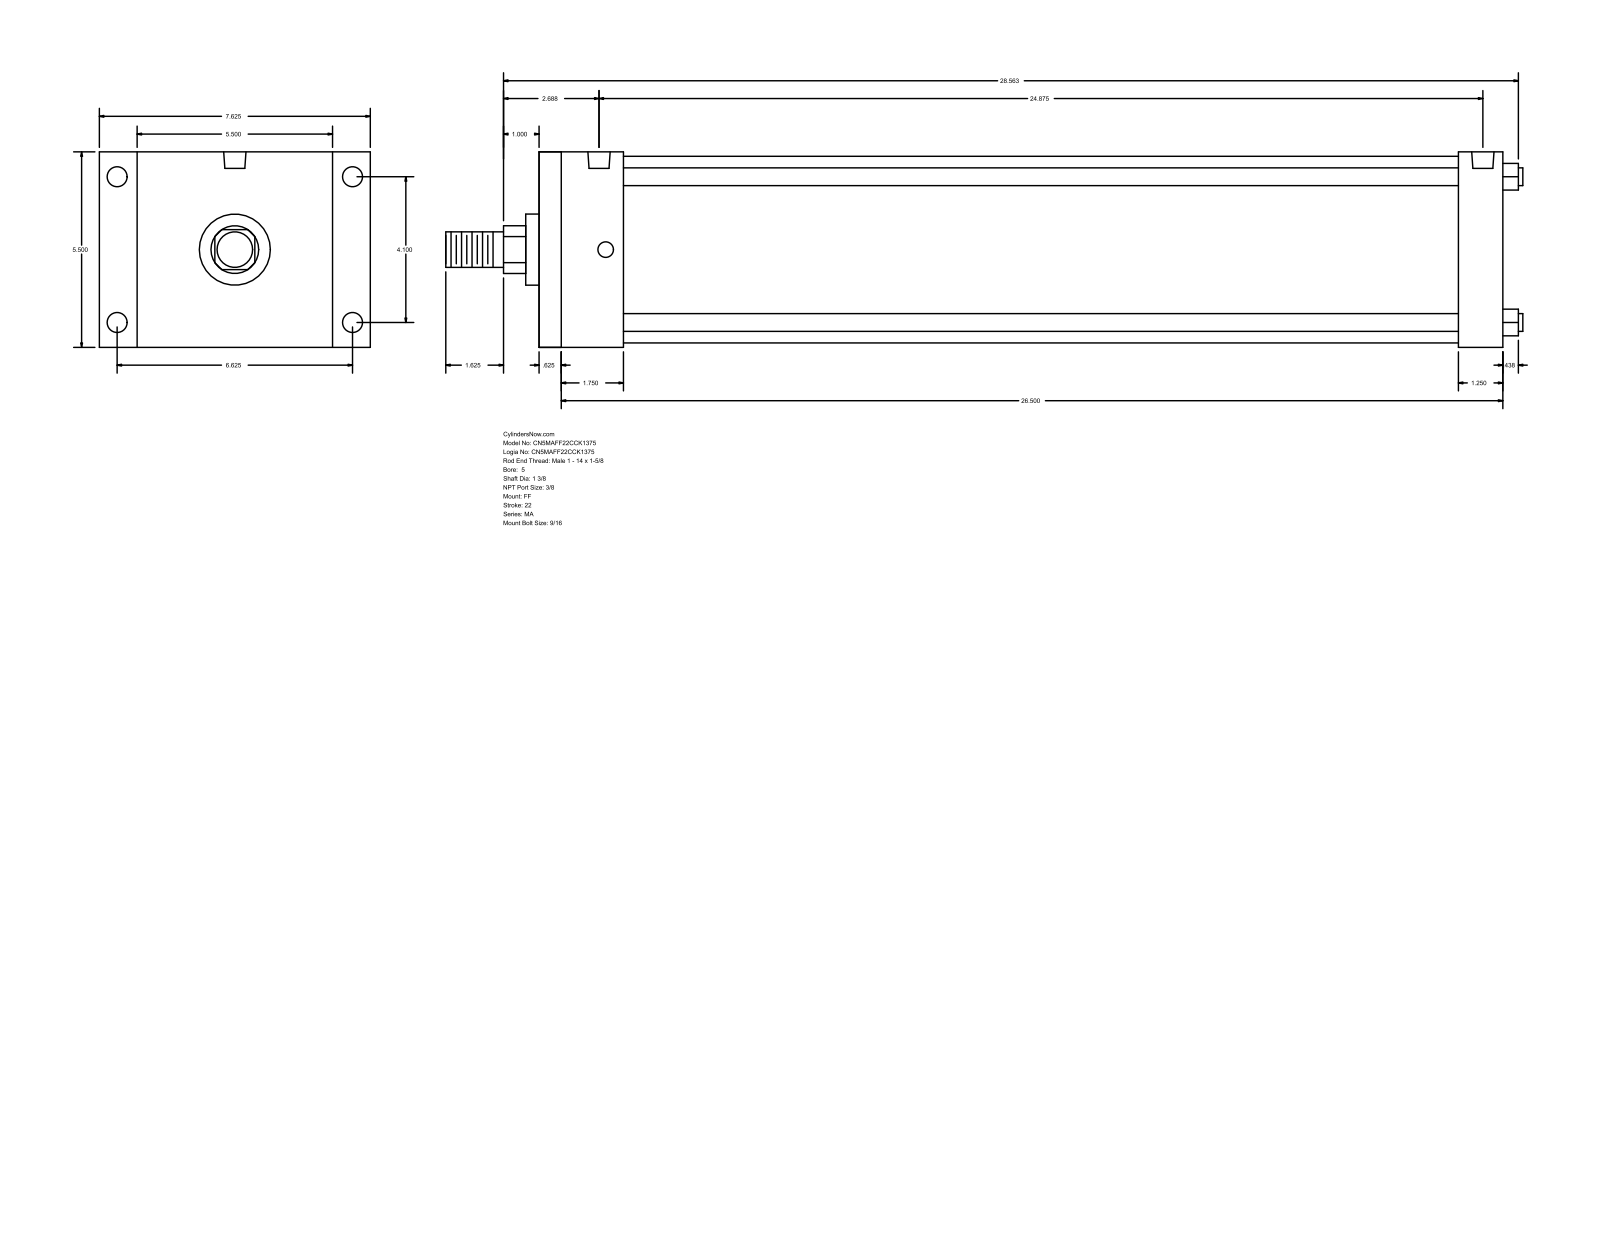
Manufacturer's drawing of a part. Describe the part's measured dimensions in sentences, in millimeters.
The part is named "MA_FF__0500_1.375". Its 3-D file was written by "GSSL Pune (CONFIG_CONTROL_DESIGN)". It is 0 solids with 92 faces: 64 planar, 28 cylindrical and 0 other. Overall it measures 769.94 by 193.68 by 139.7 millimeters. Round holes: 4 of diameter 11.11, 4 of diameter 14.29, 2 of diameter 15.93. Round bosses or shafts: 4 of diameter 12.7, 1 of diameter 133.35, 1 of diameter 50.8, 1 of diameter 34.92, 1 of diameter 25.4. Partial cylindrical surfaces (rounded edges, fillets, slot ends): 1 of radius 17.06. The main face-to-face distances are 139.7, 688.98, 15.87, 673.11, 657.22, 641.35, 31.76, 60.32, 44.45, 596.9. The hole center spacings are 104.14, 168.28, 197.9, 622.3, 4.76, 4.77, 627.06, 627.07.
